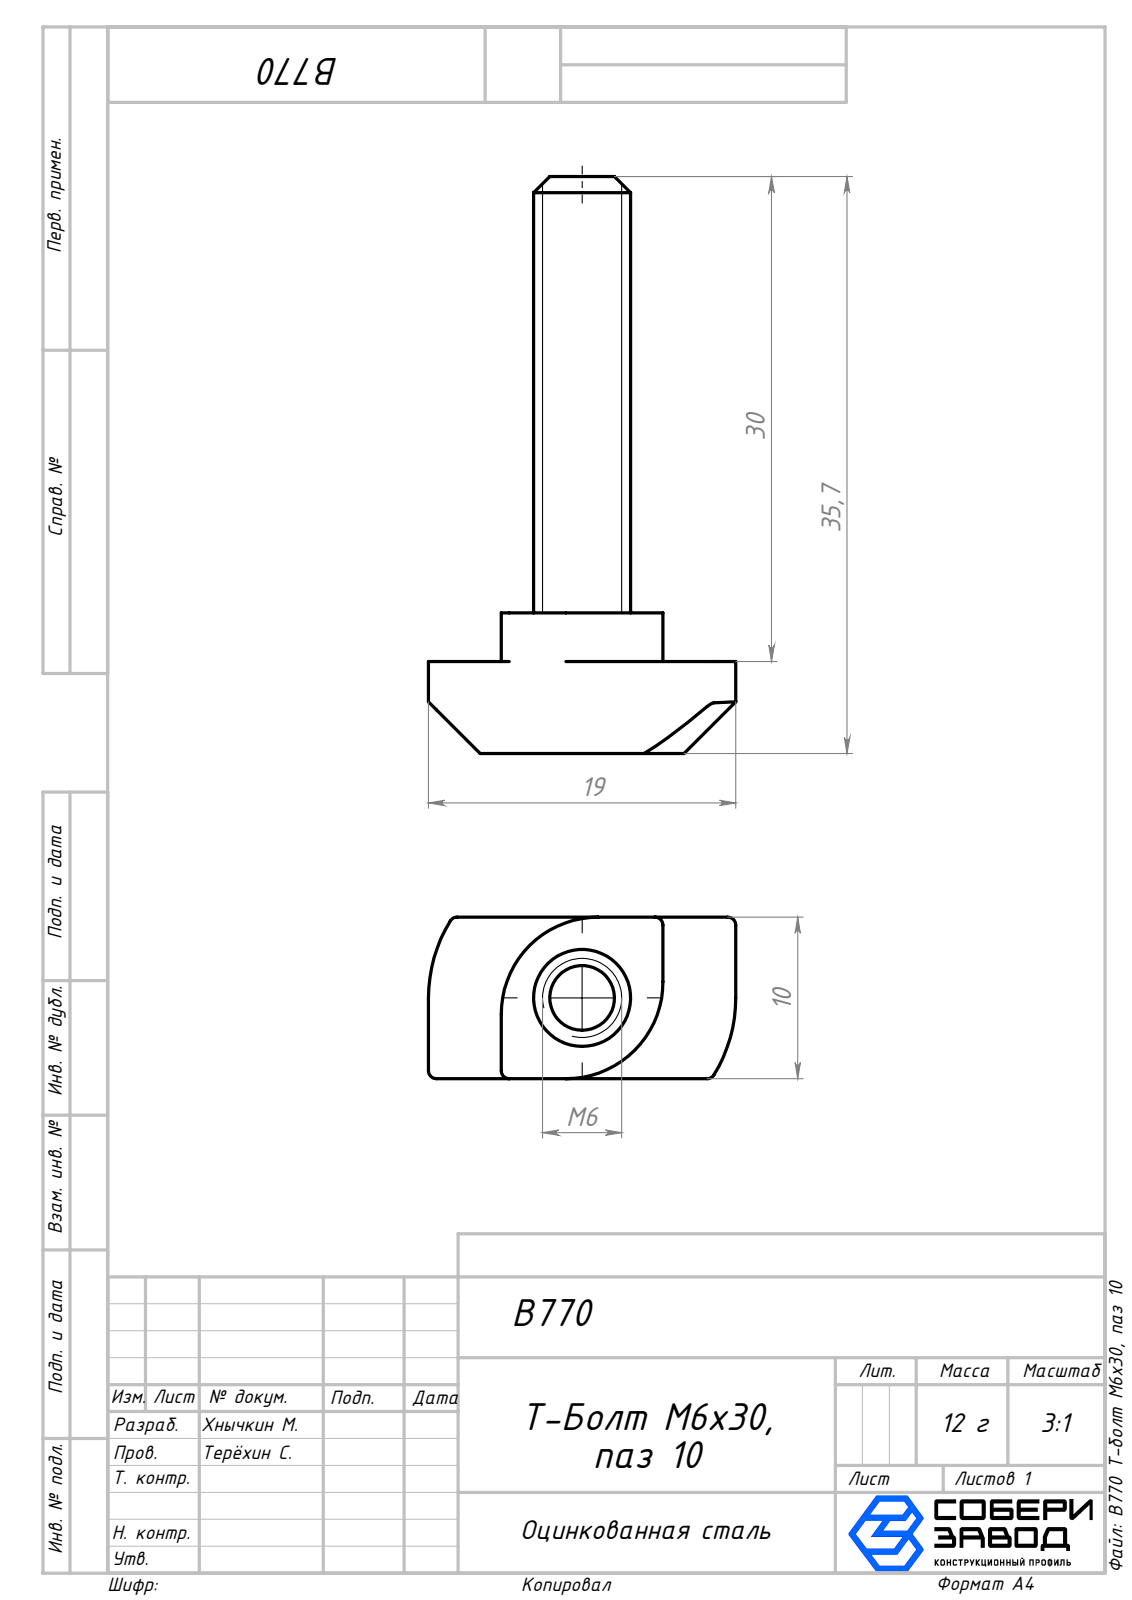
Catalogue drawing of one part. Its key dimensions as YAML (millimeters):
part_name: "B770 Т-болт М6х30, паз 10"
step_written_by: "SolidWorks 2025 (AUTOMOTIVE_DESIGN)"
units: millimeters
bodies: {solids: 1, faces: 29, planar: 13, cylindrical: 12, other: 4}
overall_size: [35.7, 19, 10]
volume: 1958
surface_area: 1225
round_bosses_or_shafts:
  - {diameter: 6, count: 1}
partial_cylinders:
  - {radius: 0.5, count: 6}
  - {radius: 6, count: 2}
  - {radius: 9.08, count: 2}
face_to_face_distances: [10, 5.7, 8.7, 3, 4.5, 14.5, 35.7, 30, 27, 19]
